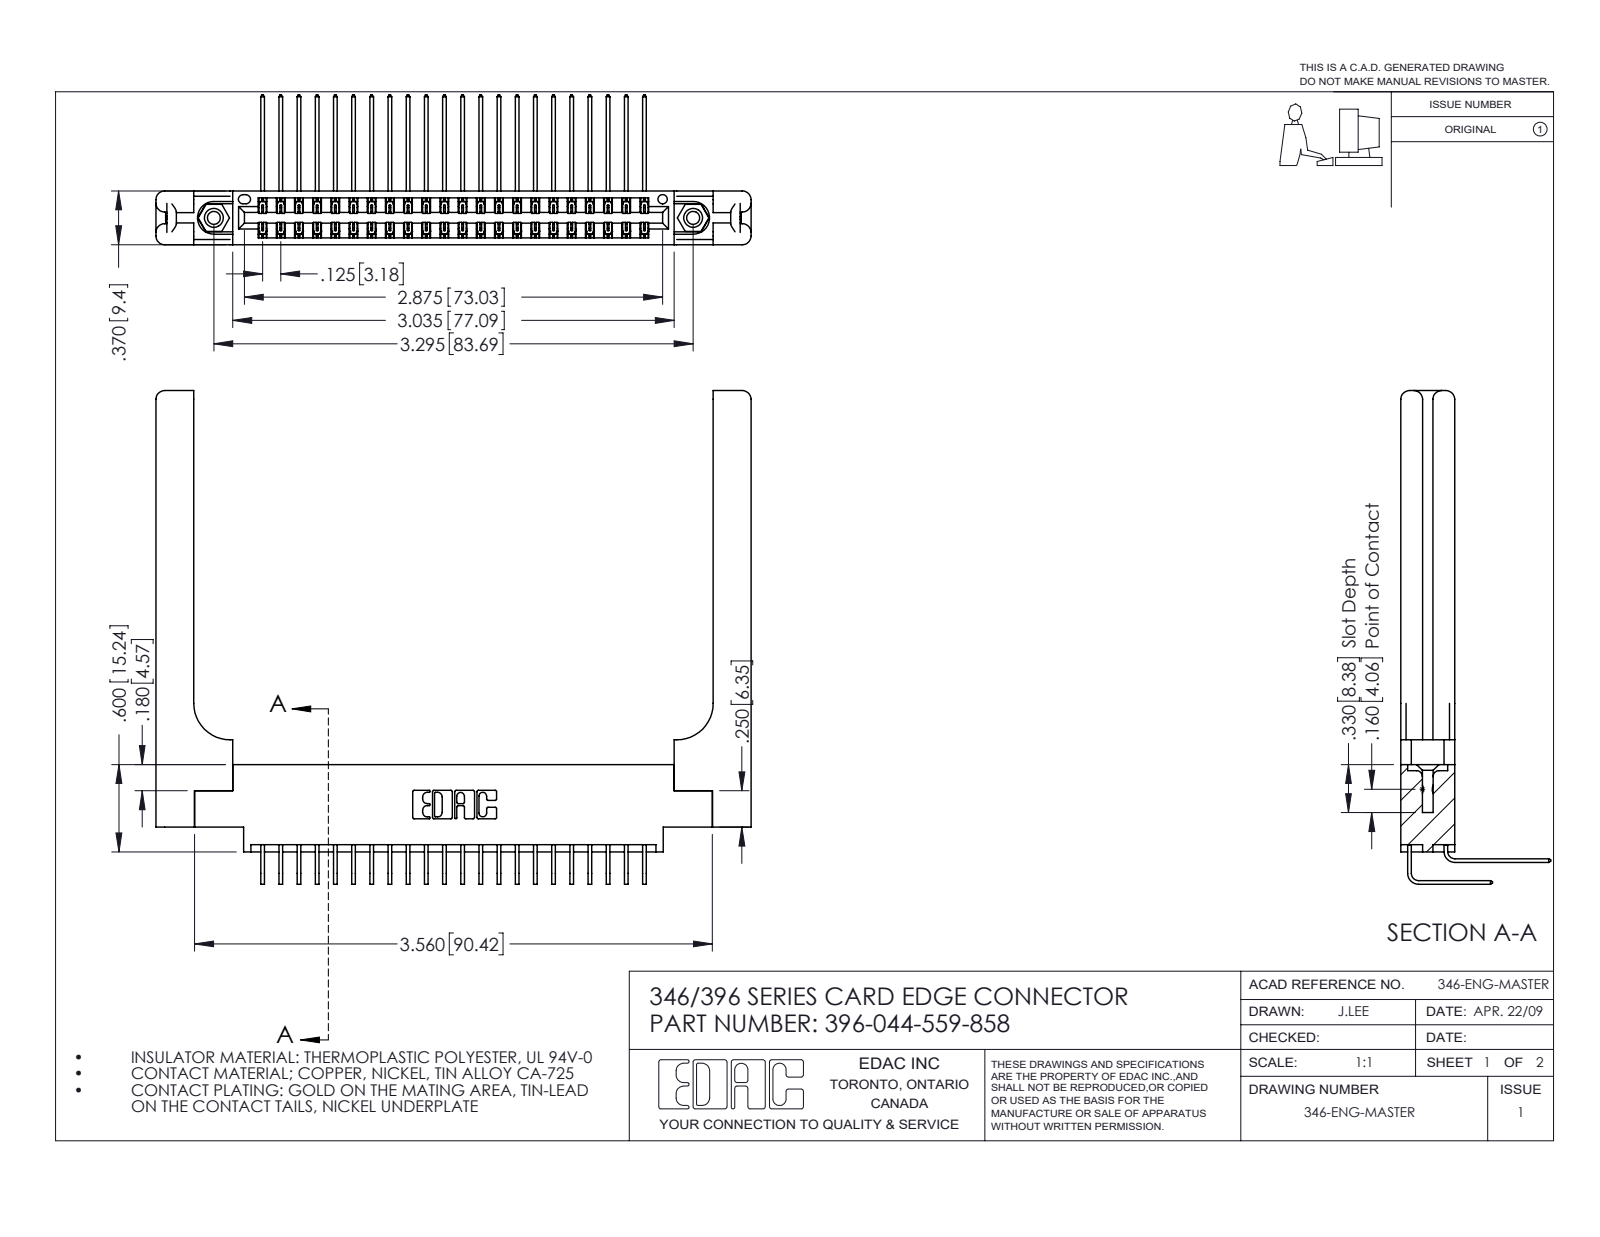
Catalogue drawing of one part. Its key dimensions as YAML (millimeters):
part_name: "345-292-001_559 Tail - 2; 396-044-559-858; 345-292-001_558 559 Tail - 1; 346-220-058_345-220-058 (+2 more)"
step_written_by: "SolidWorks 2016 (CONFIG_CONTROL_DESIGN)"
units: millimeters
bodies: {solids: 49, faces: 2758, planar: 1856, cylindrical: 842, other: 60}
overall_size: [103.9, 86.2, 26.2]
volume: 17570
surface_area: 19910
round_holes:
  - {diameter: 2.3, count: 2}
  - {diameter: 3.2, count: 2}
  - {diameter: 4, count: 2}
  - {diameter: 1.6, count: 1}
round_bosses_or_shafts:
  - {diameter: 3.9, count: 2}
partial_cylinders:
  - {radius: 0.2, count: 66}
  - {radius: 0.3, count: 22}
  - {radius: 1.5, count: 16}
  - {radius: 0.2, count: 6}
  - {radius: 0.8, count: 6}
  - {radius: 0.7, count: 3}
  - {radius: 0.4, count: 2}
  - {radius: 0.6, count: 2}
face_to_face_distances: [9.4, 1.8, 1.2, 8.2, 3.8, 3.8, 0.6, 6.4, 7.6, 2]
hole_center_spacings: [6.2, 78.4, 83.7]
